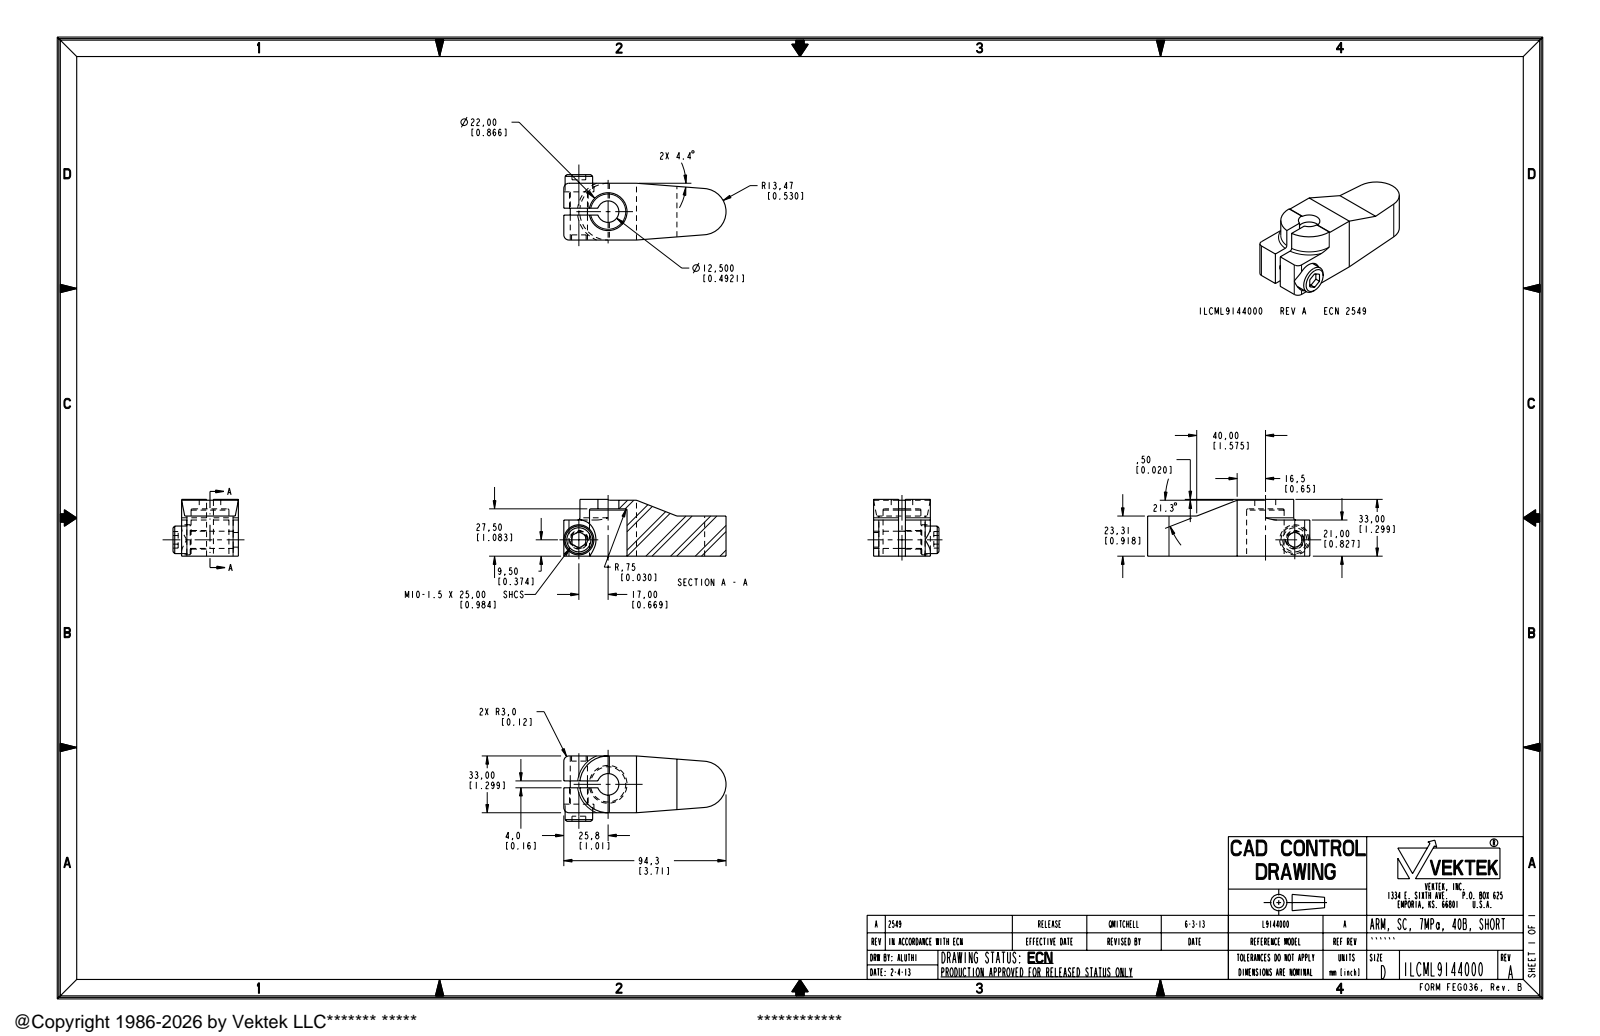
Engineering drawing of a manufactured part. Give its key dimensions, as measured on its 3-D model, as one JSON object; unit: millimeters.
{"part_name": "ILCML9144000", "step_written_by": "PRO/ENGINEER BY PARAMETRIC TECHNOLOGY CORPORATION, 2007460 (AUTOMOTIVE_DESIGN_CC2)", "units": "millimeters", "bodies": {"solids": 1, "faces": 55, "planar": 28, "cylindrical": 22, "other": 5}, "overall_size": [94.3, 38, 33], "volume_mm3": 65615, "surface_area_mm2": 16292, "round_holes": [[8.5, 1], [10.8, 1], [12.5, 1], [17.5, 1], [22, 1]], "round_bosses_or_shafts": [[16, 1], [10, 1]], "partial_cylinders_radius": [[3, 2], [0.8, 1], [13.47, 1], [16.5, 1]], "face_to_face_distances": [33, 23.31, 14.5, 18.5, 32.5, 9.19, 11.5, 5, 21, 2.31]}
